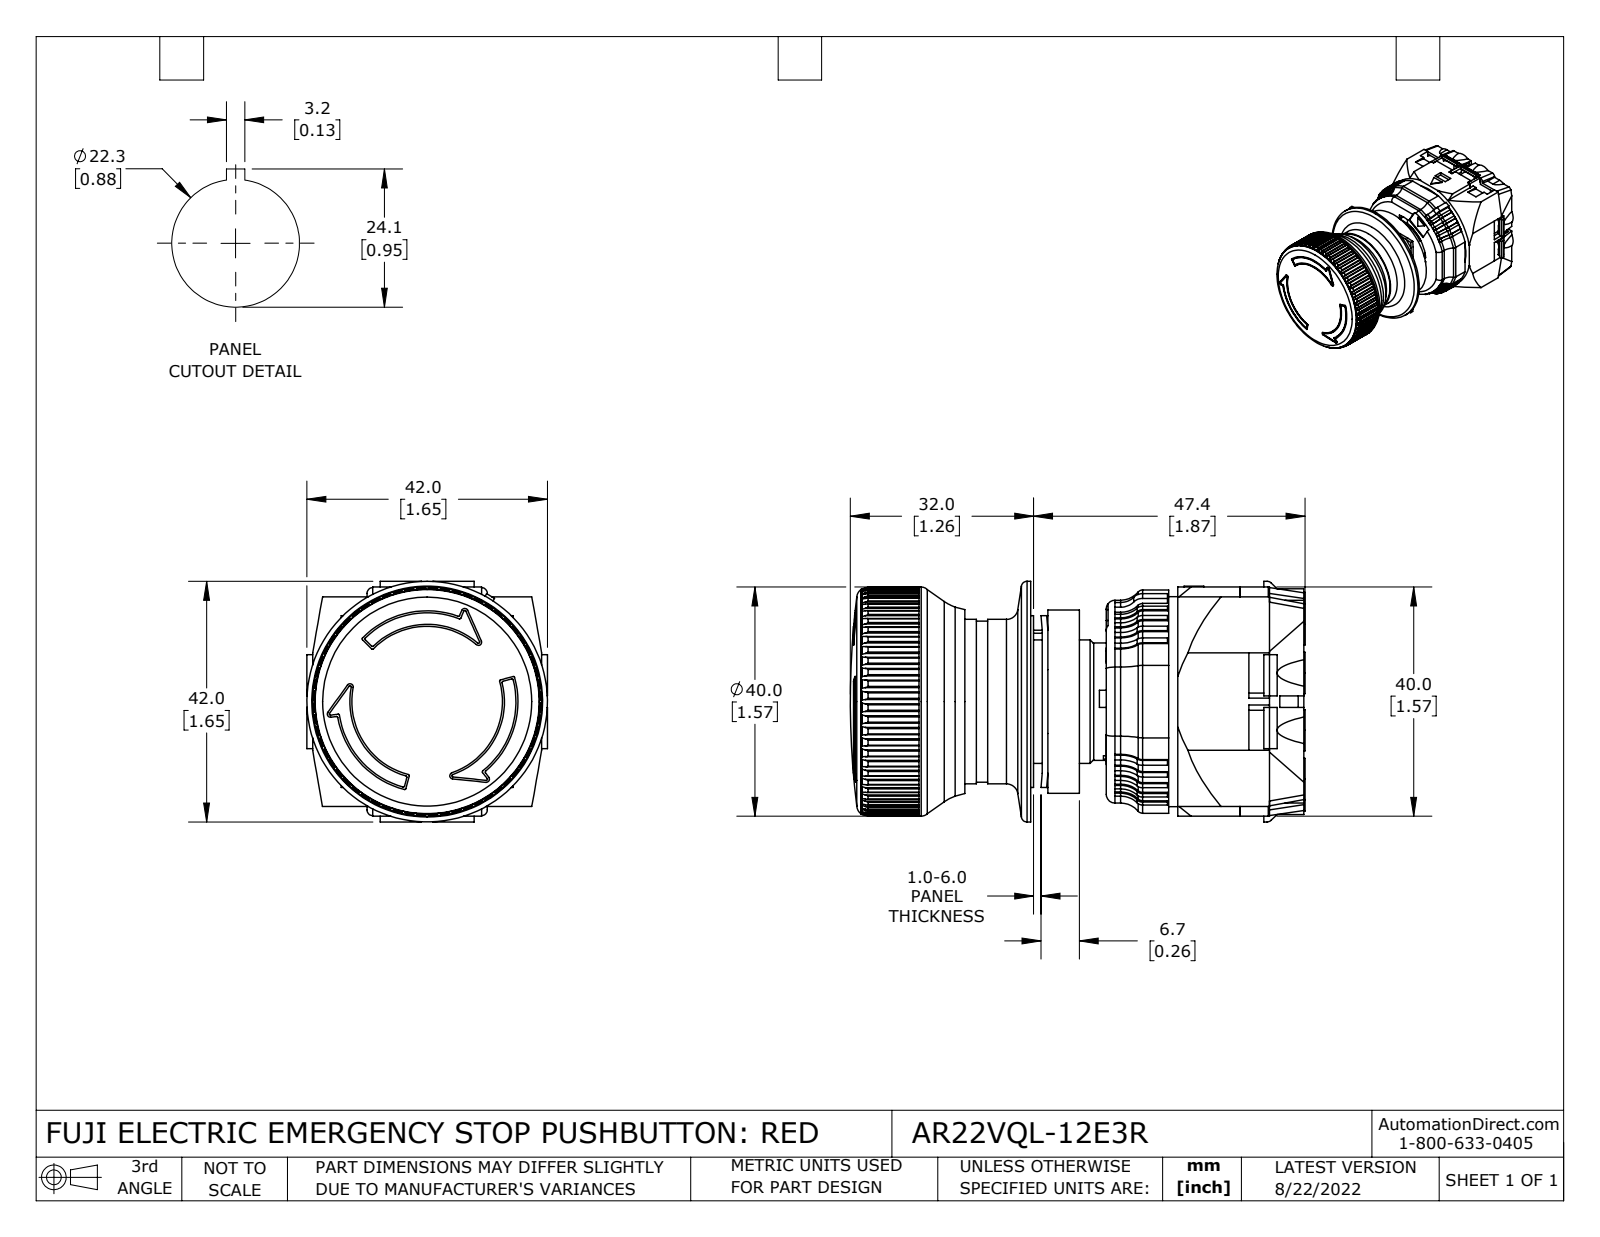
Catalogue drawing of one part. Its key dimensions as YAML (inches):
part_name: "AR22VQL-12E3R"
step_written_by: "SolidWorks 2021 (CONFIG_CONTROL_DESIGN)"
units: inches
bodies: {solids: 8, faces: 1459, planar: 645, cylindrical: 600, other: 214}
overall_size: [3.126, 1.654, 1.654]
volume: 3.81
surface_area: 53.8
round_holes:
  - {diameter: 0.138, count: 12}
  - {diameter: 0.244, count: 12}
  - {diameter: 0.315, count: 1}
  - {diameter: 0.689, count: 1}
  - {diameter: 0.827, count: 1}
  - {diameter: 0.839, count: 1}
  - {diameter: 0.866, count: 1}
  - {diameter: 0.878, count: 1}
  - {diameter: 1.102, count: 1}
  - {diameter: 1.169, count: 1}
  - {diameter: 1.443, count: 1}
round_bosses_or_shafts:
  - {diameter: 0.283, count: 12}
  - {diameter: 1.654, count: 1}
  - {diameter: 1.575, count: 1}
  - {diameter: 1.26, count: 1}
  - {diameter: 1.181, count: 1}
  - {diameter: 1.13, count: 1}
  - {diameter: 1.106, count: 1}
  - {diameter: 0.882, count: 1}
partial_cylinders:
  - {radius: 0.008, count: 146}
  - {radius: 0.016, count: 64}
  - {radius: 0.049, count: 19}
  - {radius: 0.148, count: 19}
  - {radius: 0.165, count: 12}
  - {radius: 0.039, count: 10}
  - {radius: 0.022, count: 6}
  - {radius: 0.059, count: 4}
face_to_face_distances: [0.039, 0.728, 0.453, 0.394, 1.76, 0.709, 0.827, 0.118, 0.929, 0.157]
hole_center_spacings: [0.641, 0.907, 0.325, 0.349, 0.394, 0.585, 0.713, 0.735]
